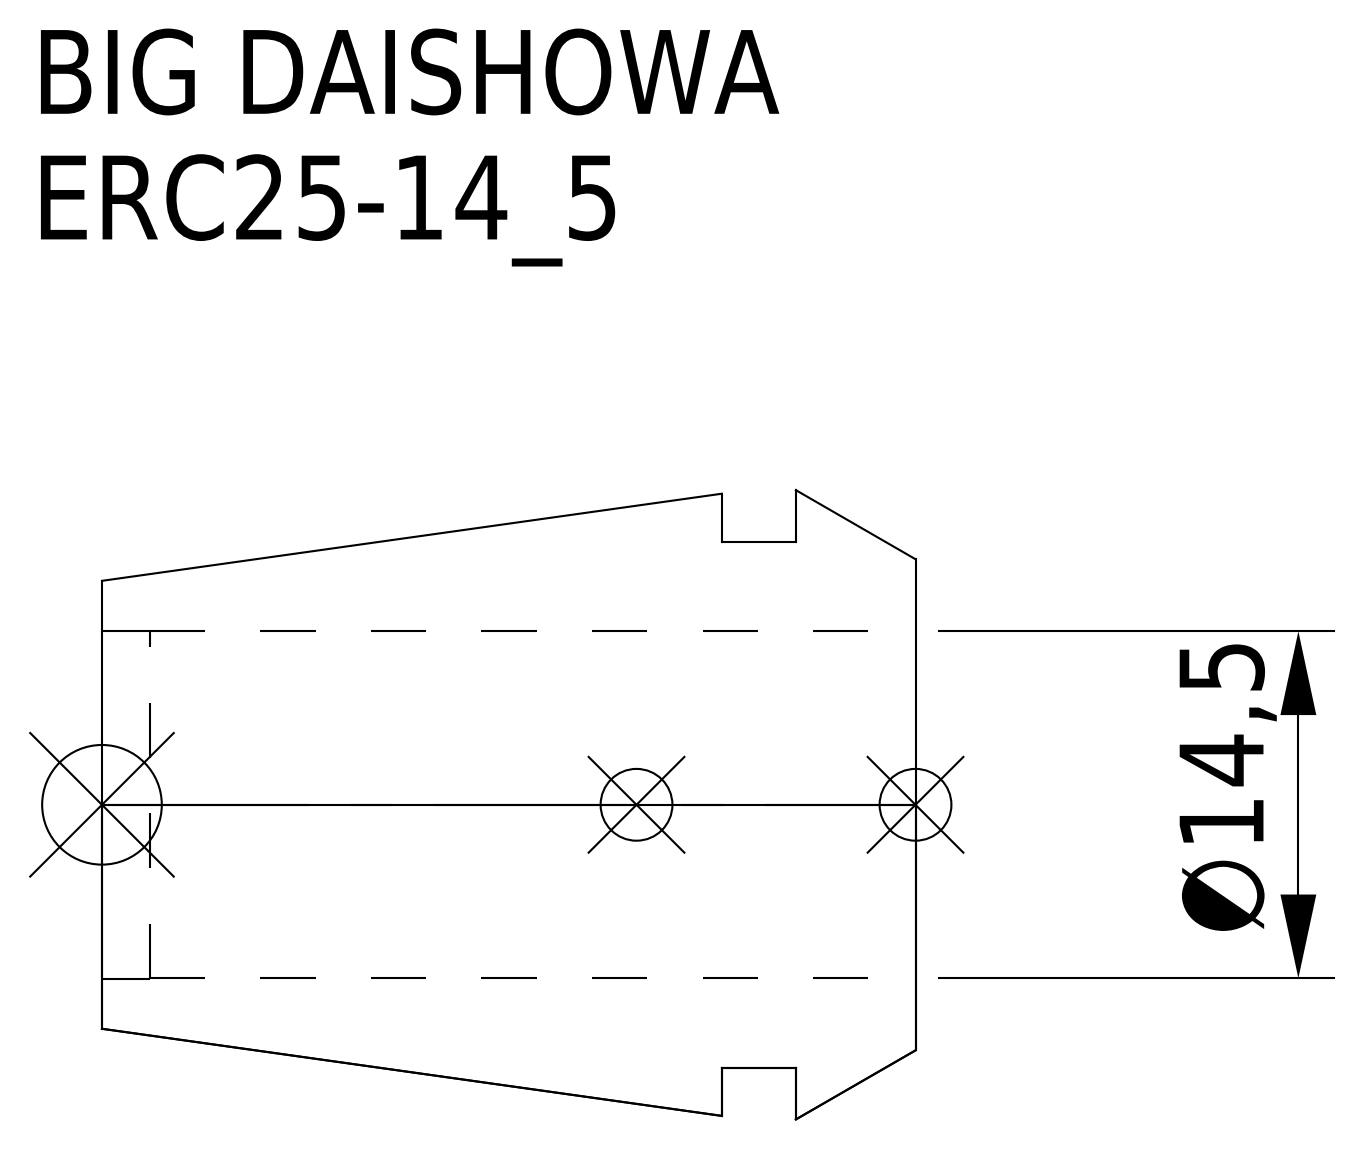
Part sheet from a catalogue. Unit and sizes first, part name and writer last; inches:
Units: inches
Overall size (bounding box): 1.339 × 1.035 × 1.035
Round holes (diameter × count): ⌀0.571 ×1, ⌀0.573 ×1
Round bosses / shafts (diameter × count): ⌀0.866 ×1
Main face-to-face distances: 0.197, 0.319, 0.122, 1.339, 1.142, 1.02, 1.26, 1.063, 0.941, 0.079
Volume: 0.487 in³ · Surface area: 7.153 in²
Bodies: 1 solid, 15 faces (5 planar, 6 cylindrical, 4 other)
Part name (STEP PRODUCT): ERC25-14_5
STEP written by: CREO PARAMETRIC BY PTC INC, 2016380 (AUTOMOTIVE_DESIGN)
